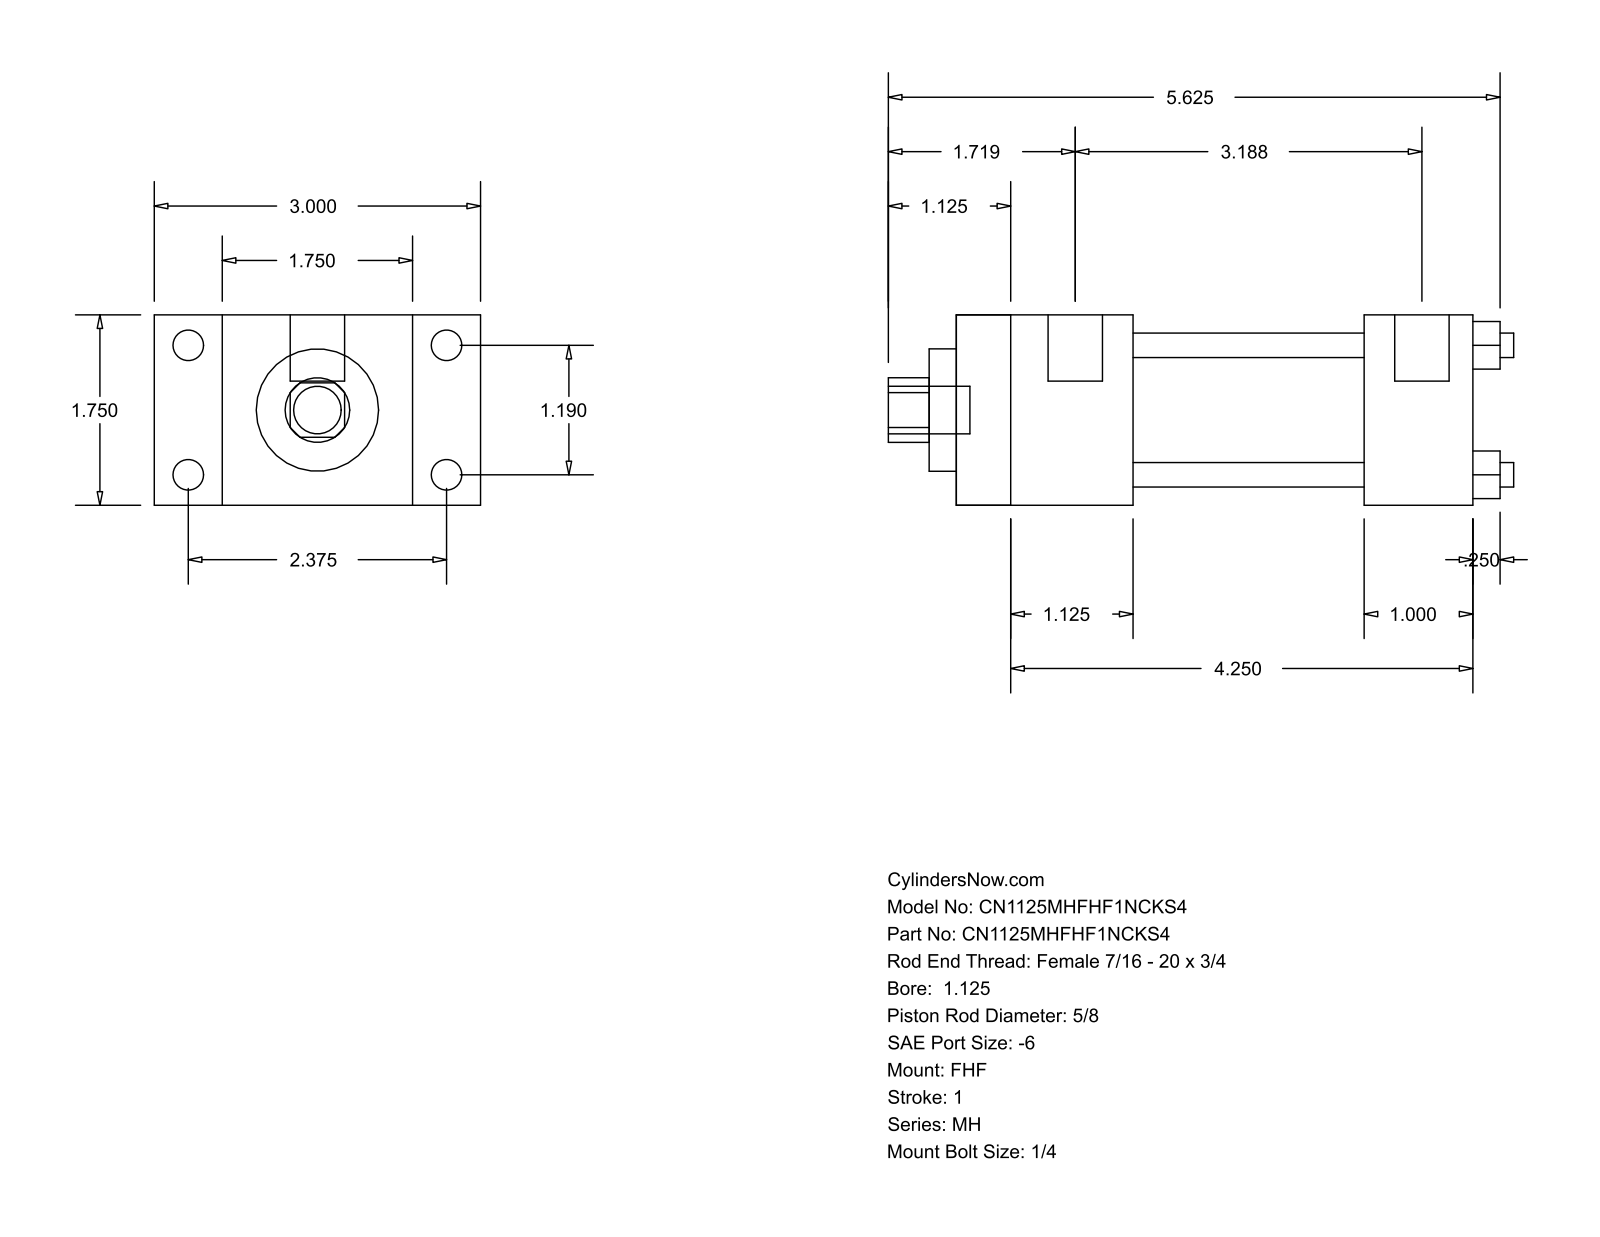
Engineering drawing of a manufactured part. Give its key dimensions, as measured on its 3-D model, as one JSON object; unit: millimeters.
{"part_name": "MH_FHF__0112_0.625", "step_written_by": "GSSL Pune (CONFIG_CONTROL_DESIGN)", "units": "millimeters", "bodies": {"solids": 0, "faces": 88, "planar": 60, "cylindrical": 28, "other": 0}, "overall_size": [146.05, 76.2, 44.45], "round_holes": [[5.71, 4], [15.88, 1], [28.57, 1], [34.92, 1]], "round_bosses_or_shafts": [[7.14, 4], [5.56, 4], [12.7, 2], [11.11, 1]], "partial_cylinders_radius": [[7.54, 1]], "face_to_face_distances": [44.46, 15.87, 60.33, 41.27, 76.2, 120.65, 79.38, 95.24, 53.97, 25.41], "hole_center_spacings": [21.37, 30.22, 42.74]}
